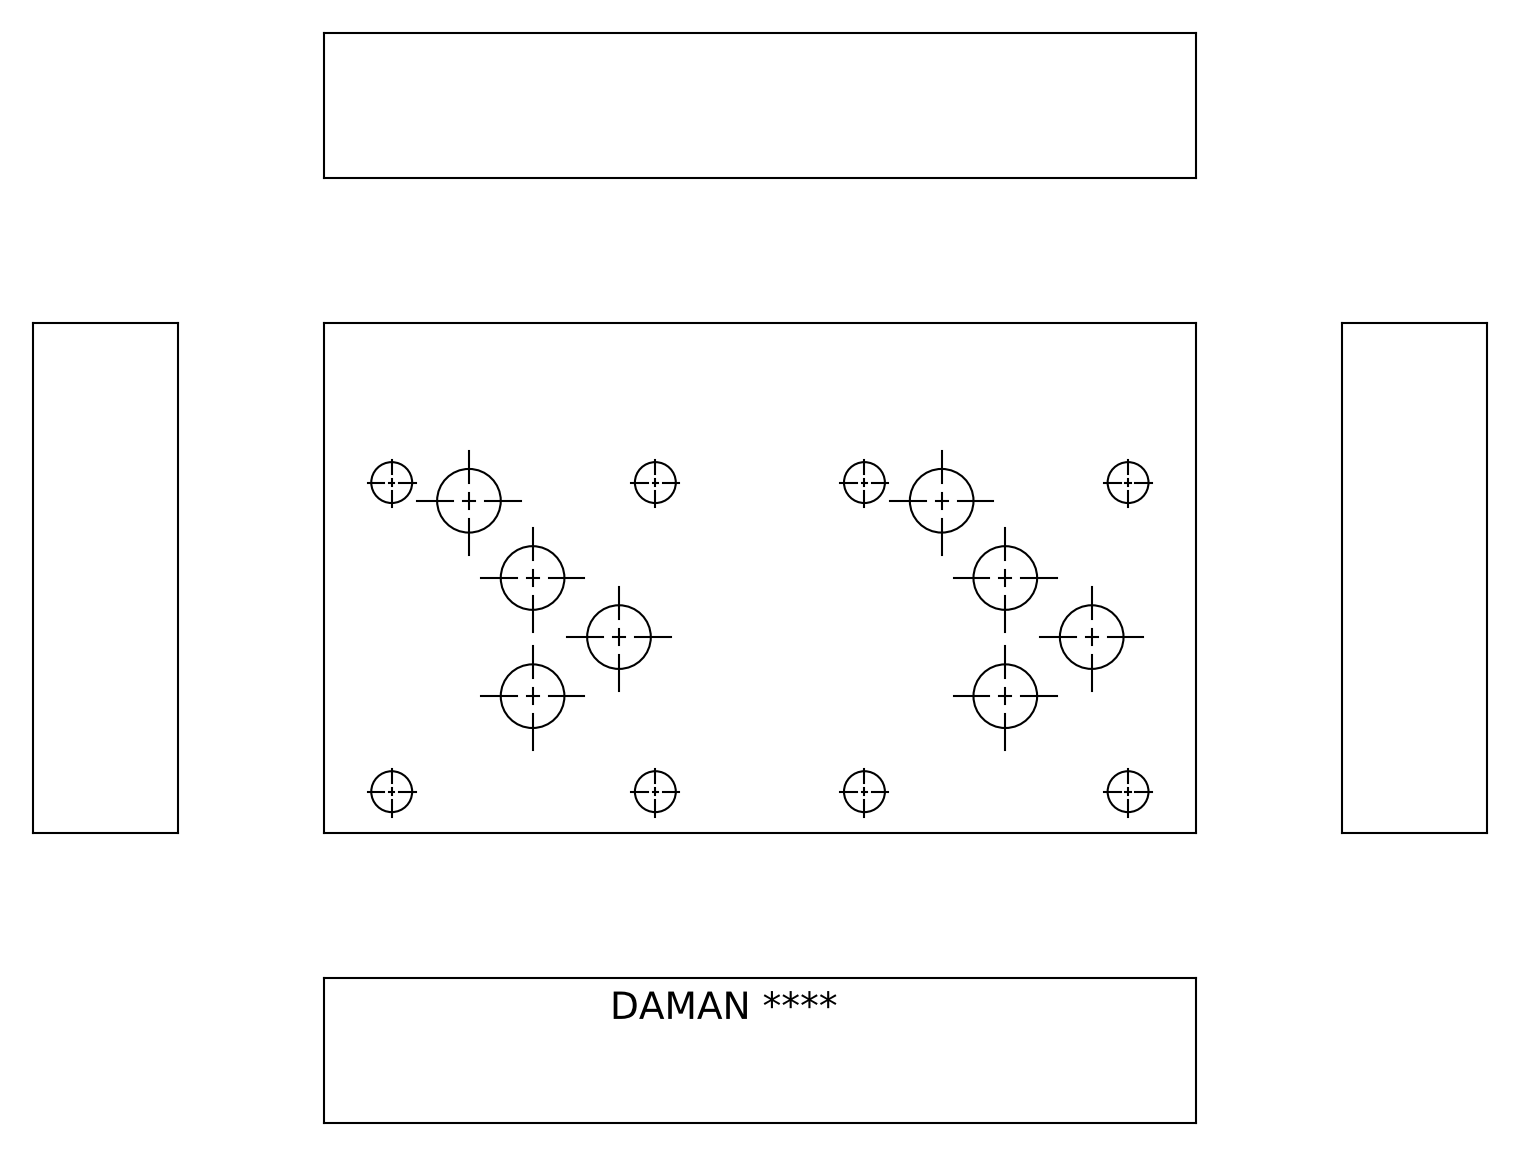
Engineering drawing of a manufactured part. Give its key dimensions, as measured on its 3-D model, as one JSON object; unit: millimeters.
{"part_name": "Part_AD05TP023AB.C08635R4_3D", "step_written_by": "Autodesk Inventor 2022 (AUTOMOTIVE_DESIGN)", "units": "millimeters", "bodies": {"solids": 1, "faces": 426, "planar": 251, "cylindrical": 44, "other": 131}, "overall_size": [152.4, 88.9, 25.4], "volume_mm3": 326920, "surface_area_mm2": 45869, "round_holes": [[11.13, 11], [15.88, 10], [7.14, 8], [11.11, 5]], "partial_cylinders_radius": [[3.57, 6]], "face_to_face_distances": [25.4, 88.9, 152.4, 1.32, 24.08, 88.86, 0.64, 3.62, 0.6, 7.84], "hole_center_spacings": [82.55, 82.56, 20.62, 17.49, 18.28, 35.87, 82.57, 17.48]}
